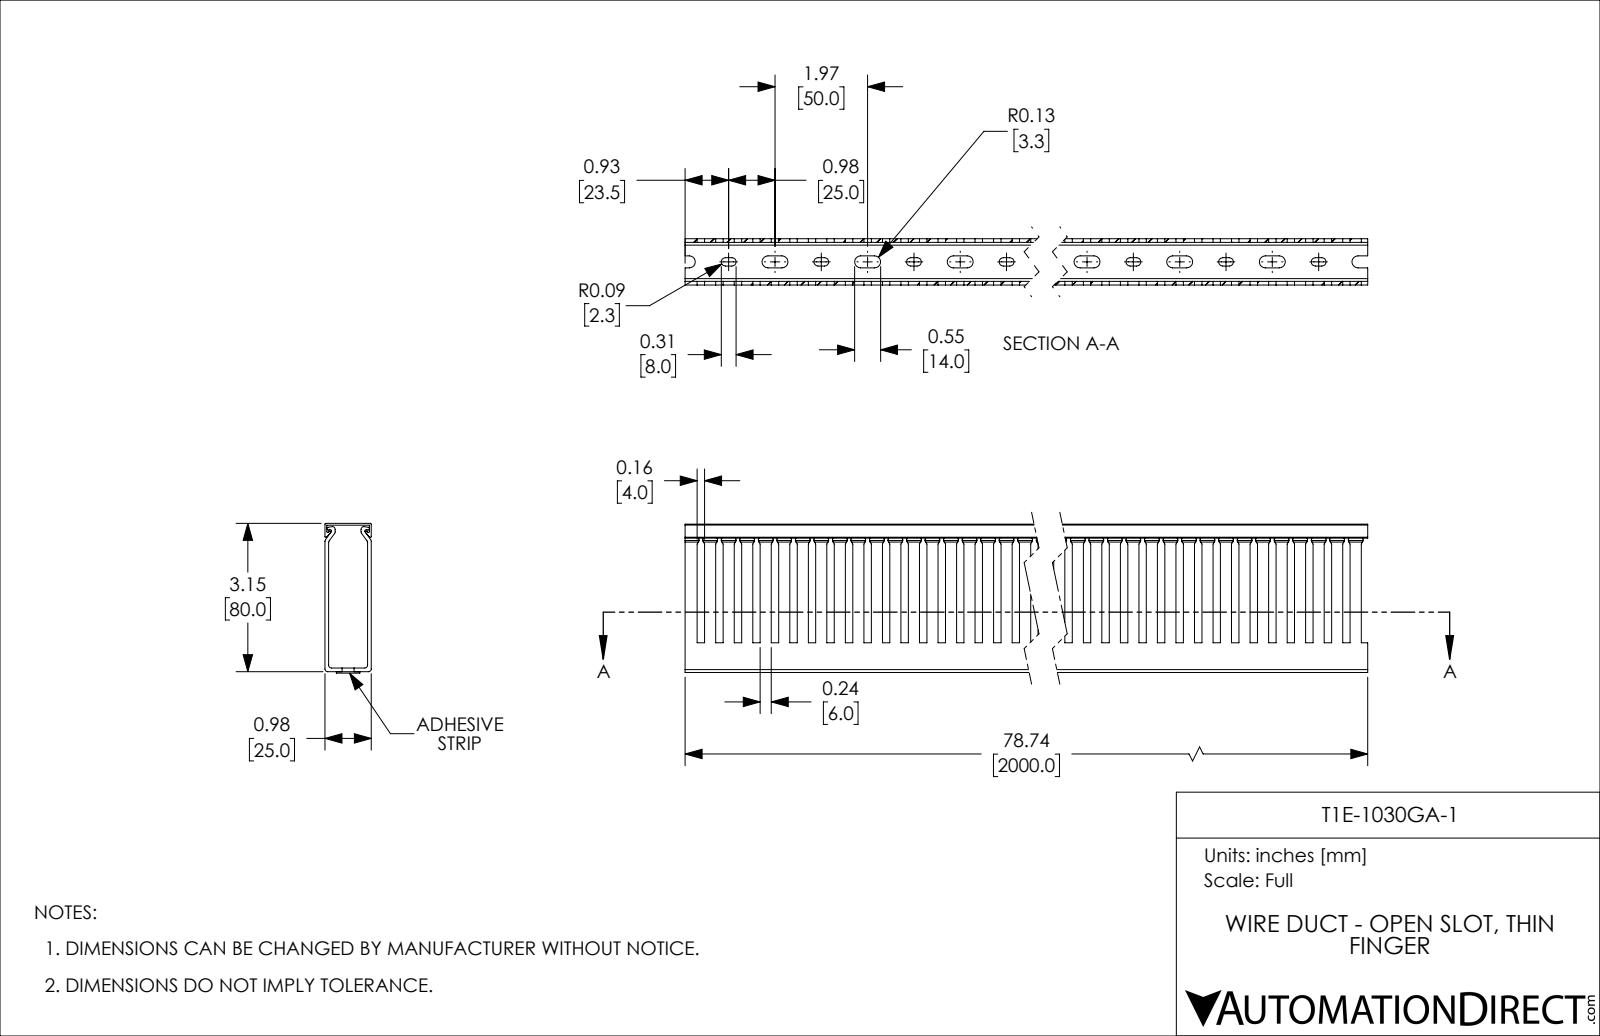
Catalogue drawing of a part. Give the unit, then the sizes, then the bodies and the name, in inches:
Units: inches
Overall size (bounding box): 78.74 × 3.181 × 0.984
Partial cylindrical surfaces — rounded edges, fillets, slot ends (radius × count): R0.089 ×80, R0.128 ×80, R0.059 ×12, R0.02 ×8, R0.03 ×6
Main face-to-face distances: 0.079, 0.906, 0.984, 0.827, 0.039, 3.15, 3.11, 3.031, 3.071, 0.031
Volume: 50.14 in³ · Surface area: 1 470 in²
Bodies: 3 solids, 951 faces (520 planar, 431 cylindrical, 0 other)
Part name (STEP PRODUCT): T1E-1030GA-1
STEP written by: SolidWorks 2021 (CONFIG_CONTROL_DESIGN)
